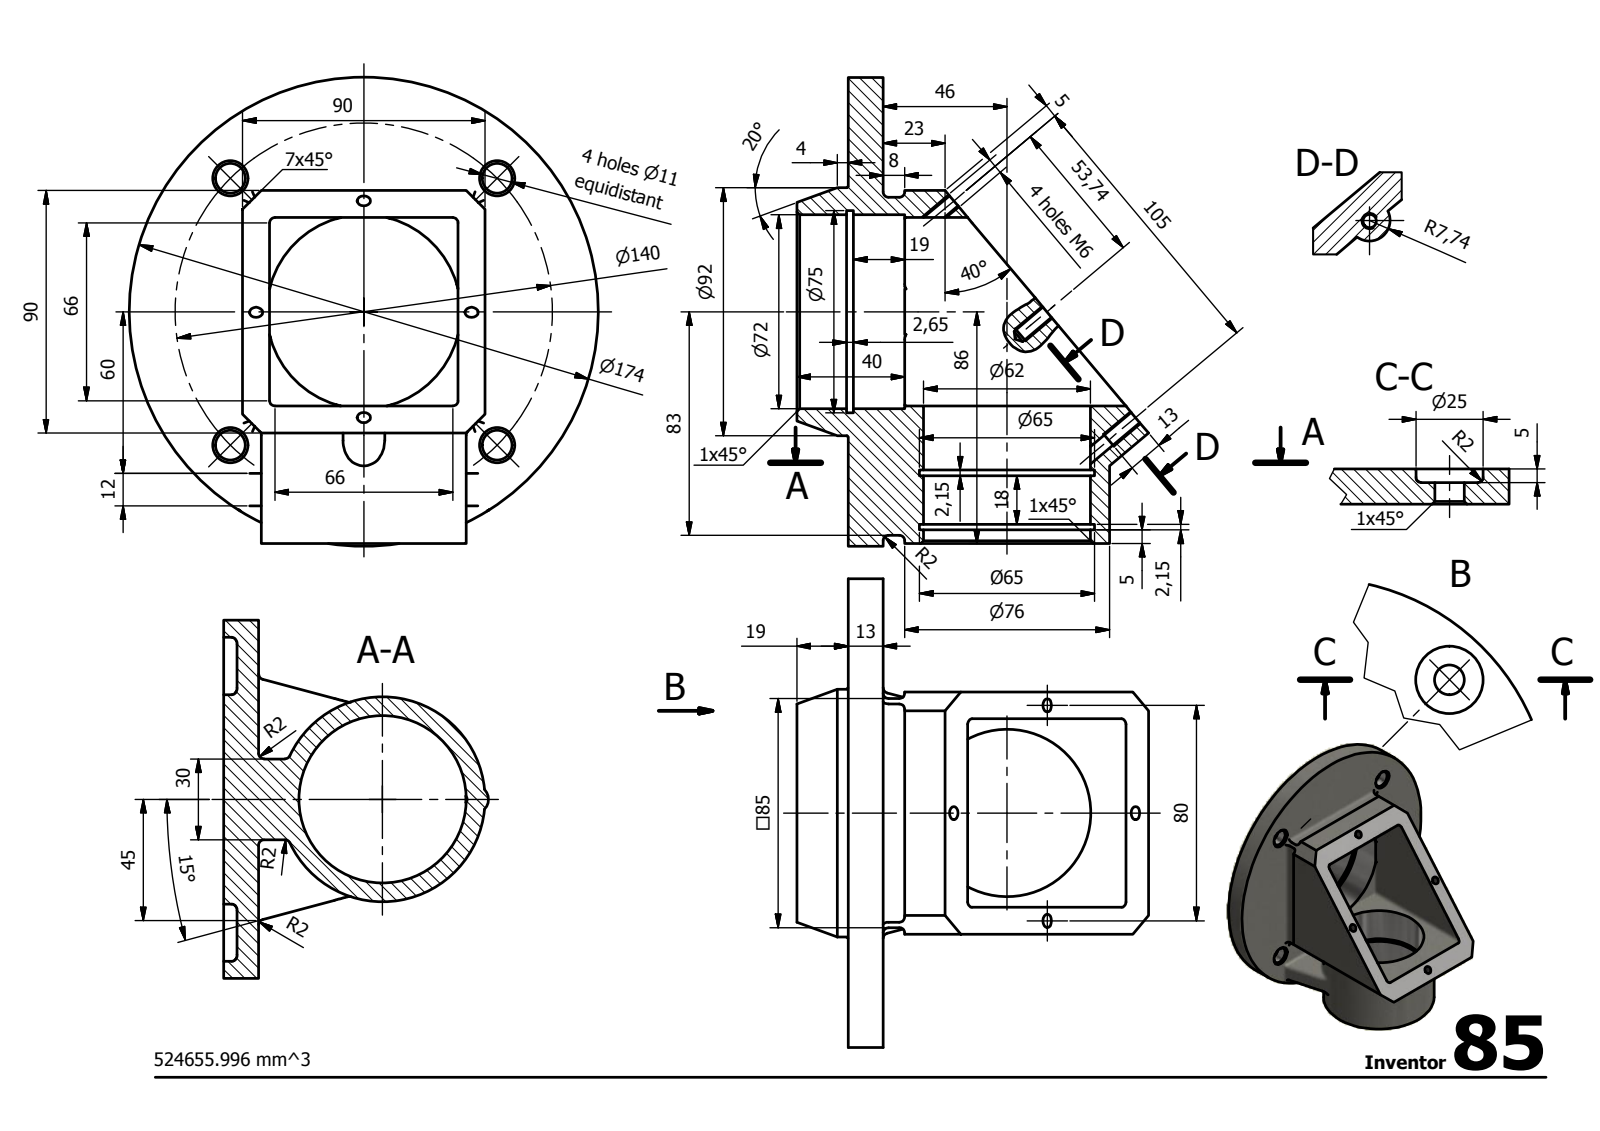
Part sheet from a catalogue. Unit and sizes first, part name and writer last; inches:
Units: inches
Overall size (bounding box): 6.85 × 6.85 × 5.139
Round holes (diameter × count): ⌀0.194 ×4, ⌀0.433 ×4, ⌀0.984 ×4, ⌀2.441 ×1, ⌀2.559 ×1, ⌀2.835 ×1, ⌀2.953 ×1
Round bosses / shafts (diameter × count): ⌀6.85 ×1, ⌀3.622 ×1, ⌀2.992 ×1
Partial cylindrical surfaces — rounded edges, fillets, slot ends (radius × count): R0.079 ×42, R0.02 ×4, R0.305 ×1
Main face-to-face distances: 0.512, 0.394, 3.15, 3.543, 2.756, 0.315, 0.827, 1.614, 2.008, 4.764
Hole centre spacings: 2.756, 3.898, 2.55, 2.646, 5.512, 3.15, 4.132
Volume: 32.02 in³ · Surface area: 176.4 in²
Bodies: 1 solid, 210 faces (58 planar, 83 cylindrical, 69 other)
STEP written by: Autodesk Inventor 2014 (AUTOMOTIVE_DESIGN)
